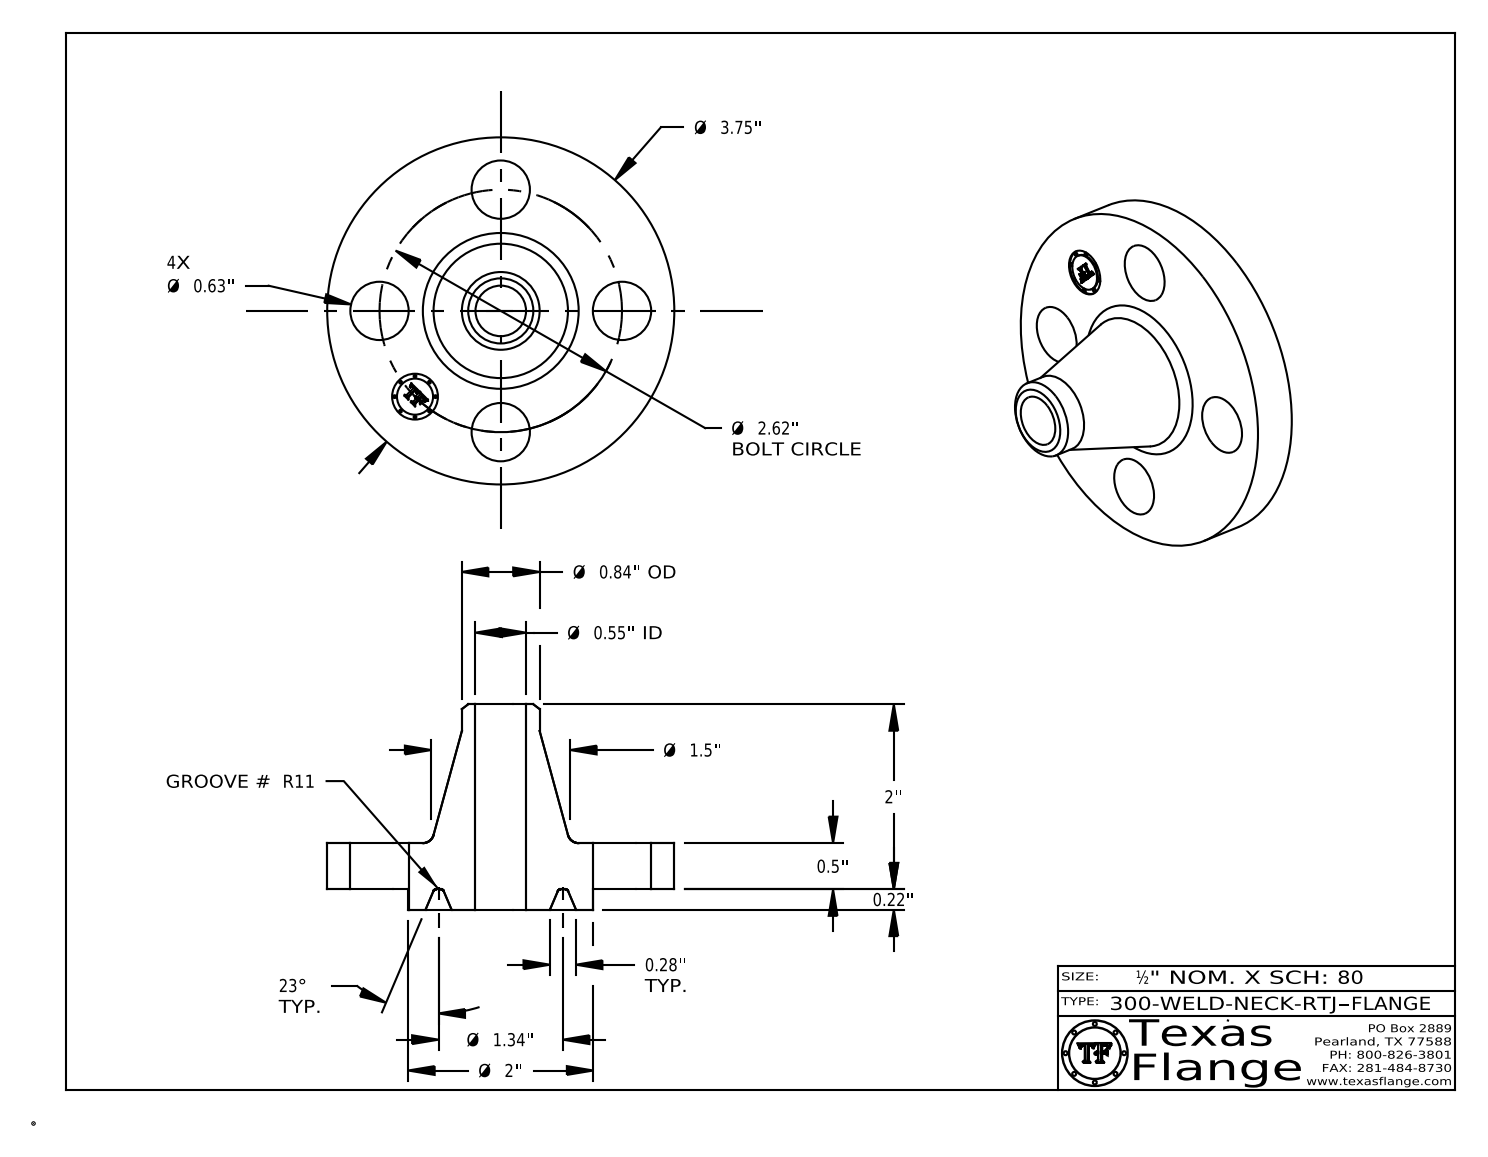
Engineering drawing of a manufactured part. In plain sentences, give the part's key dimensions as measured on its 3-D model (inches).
The part is named "300-WELD-NECK-RTJ". Its 3-D file was written by "CATIA V5 STEP AP214 (AUTOMOTIVE_DESIGN)". It is 1 solid with 425 faces: 371 planar, 40 cylindrical and 14 other. Overall it measures 3.75 by 3.75 by 2.219 inches. Its volume is 6.393 cubic inches and its surface area 39.38 square inches. Round holes: 4 of diameter 0.63, 1 of diameter 0.495, 1 of diameter 0.546. Round bosses or shafts: 8 of diameter 0.03, 1 of diameter 3.75, 1 of diameter 2, 1 of diameter 0.84, 1 of diameter 0.39. The main face-to-face distances are 0.5, 0.219, 0.719, 2.219, 2, 1.5, 0.704, 0.485, 0.015, 1.515. The hole center spacings are 1.31, 1.852, 1.003, 2.42, 2.62, 1.31.
